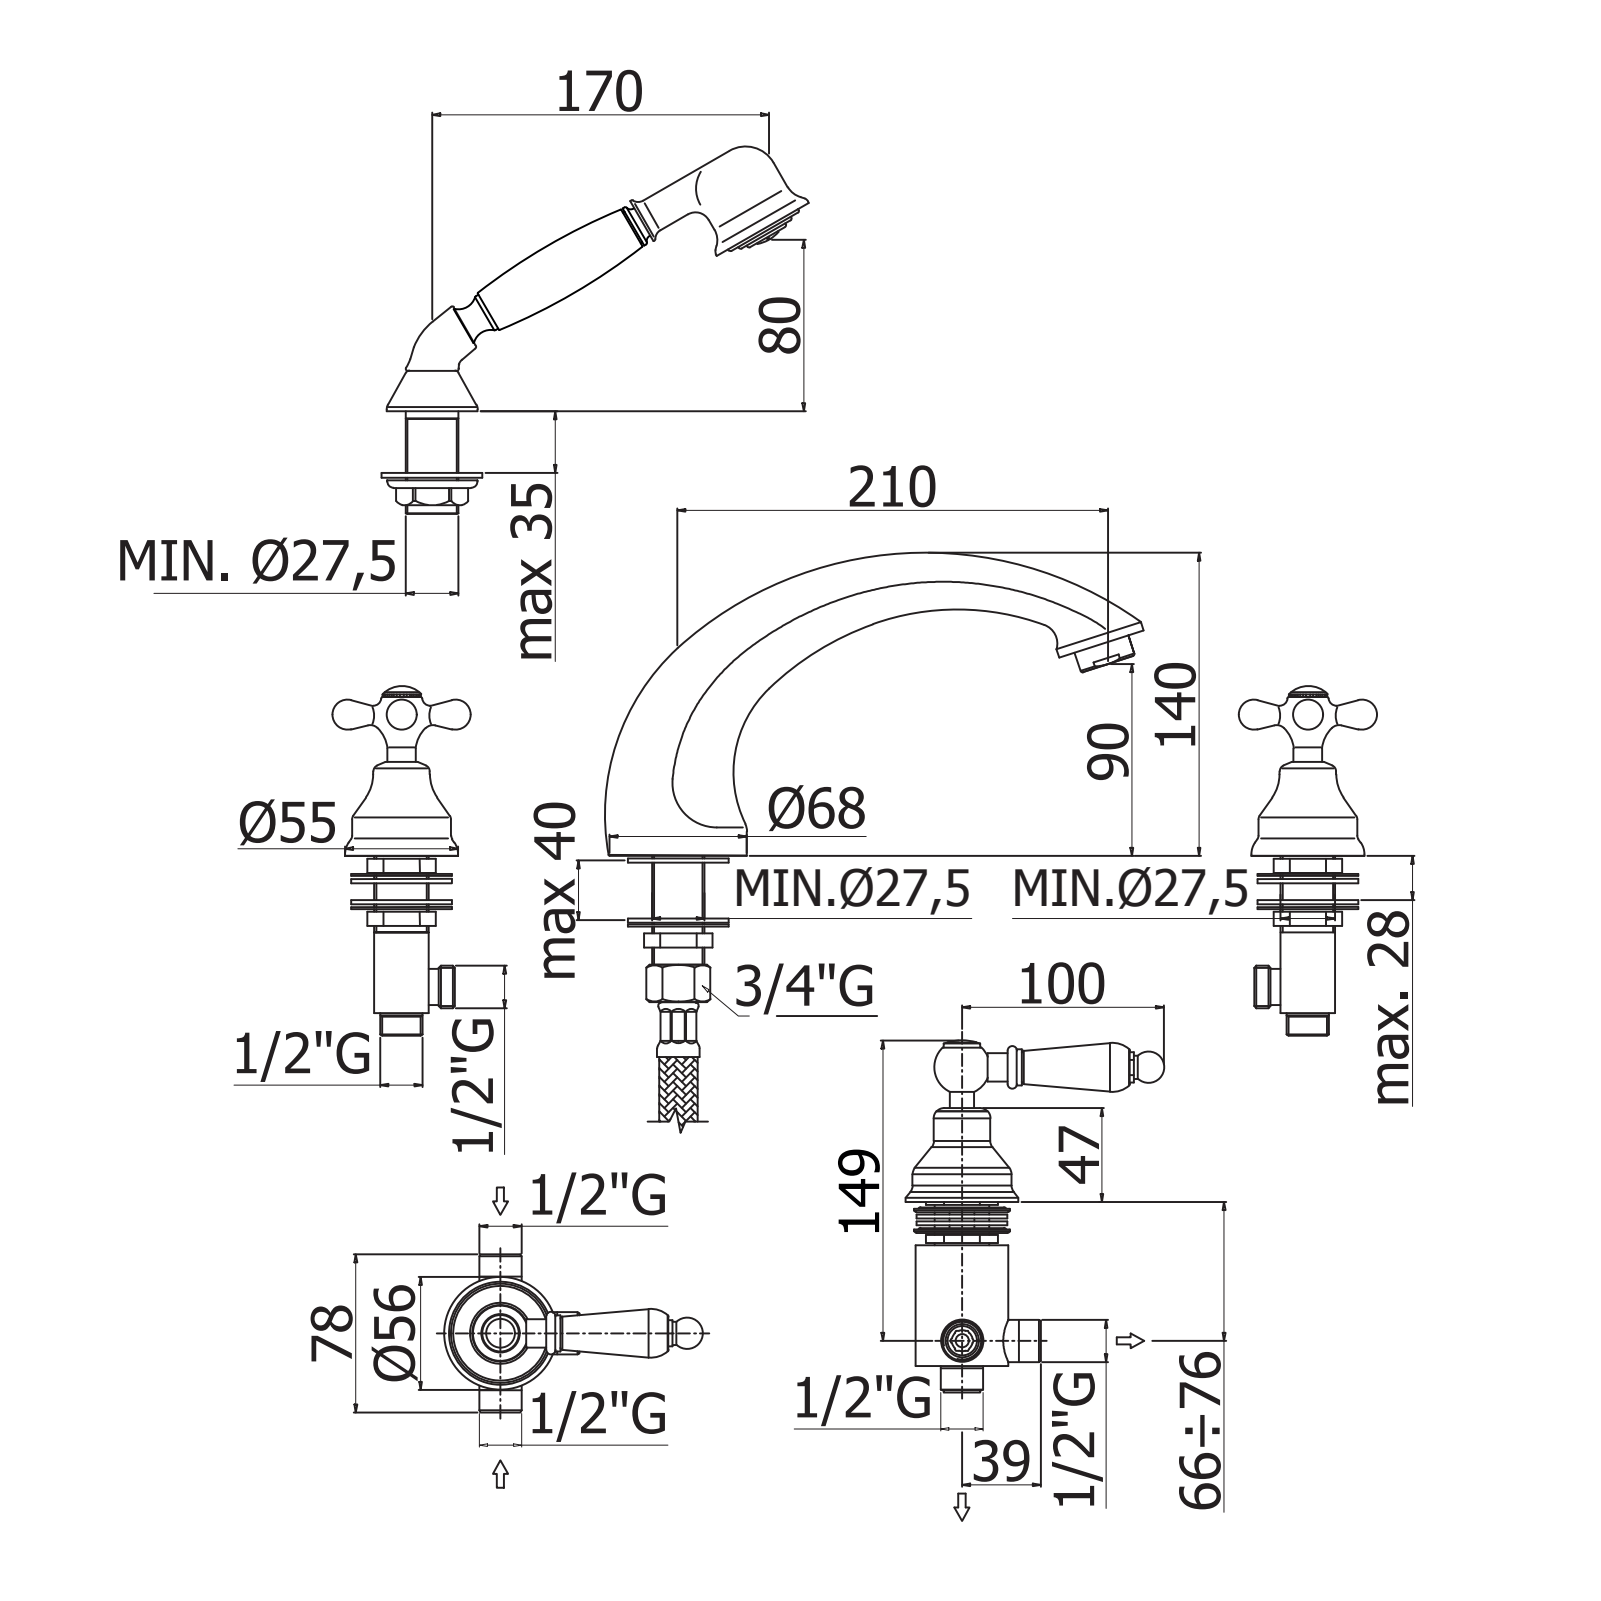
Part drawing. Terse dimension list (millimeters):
name: IRV044CR
written by: CREO PARAMETRIC BY PTC INC, 2020044 (CONFIG_CONTROL_DESIGN)
unit: mm
bodies: 5 solids, 354 faces (42 planar, 64 cylindrical, 248 other)
size: 460.5 × 267.6 × 150.84
volume: 951 011 mm³; area: 132 988 mm²
holes: 1× ⌀14.5
bosses: 4× ⌀28, 3× ⌀55, 3× ⌀49, 3× ⌀18, 2× ⌀14, 2× ⌀13.5, 1× ⌀53, 1× ⌀46
face distances: 6, 10, 46.5, 2, 15.7, 30.8, 4, 1, 103.99, 104.99
